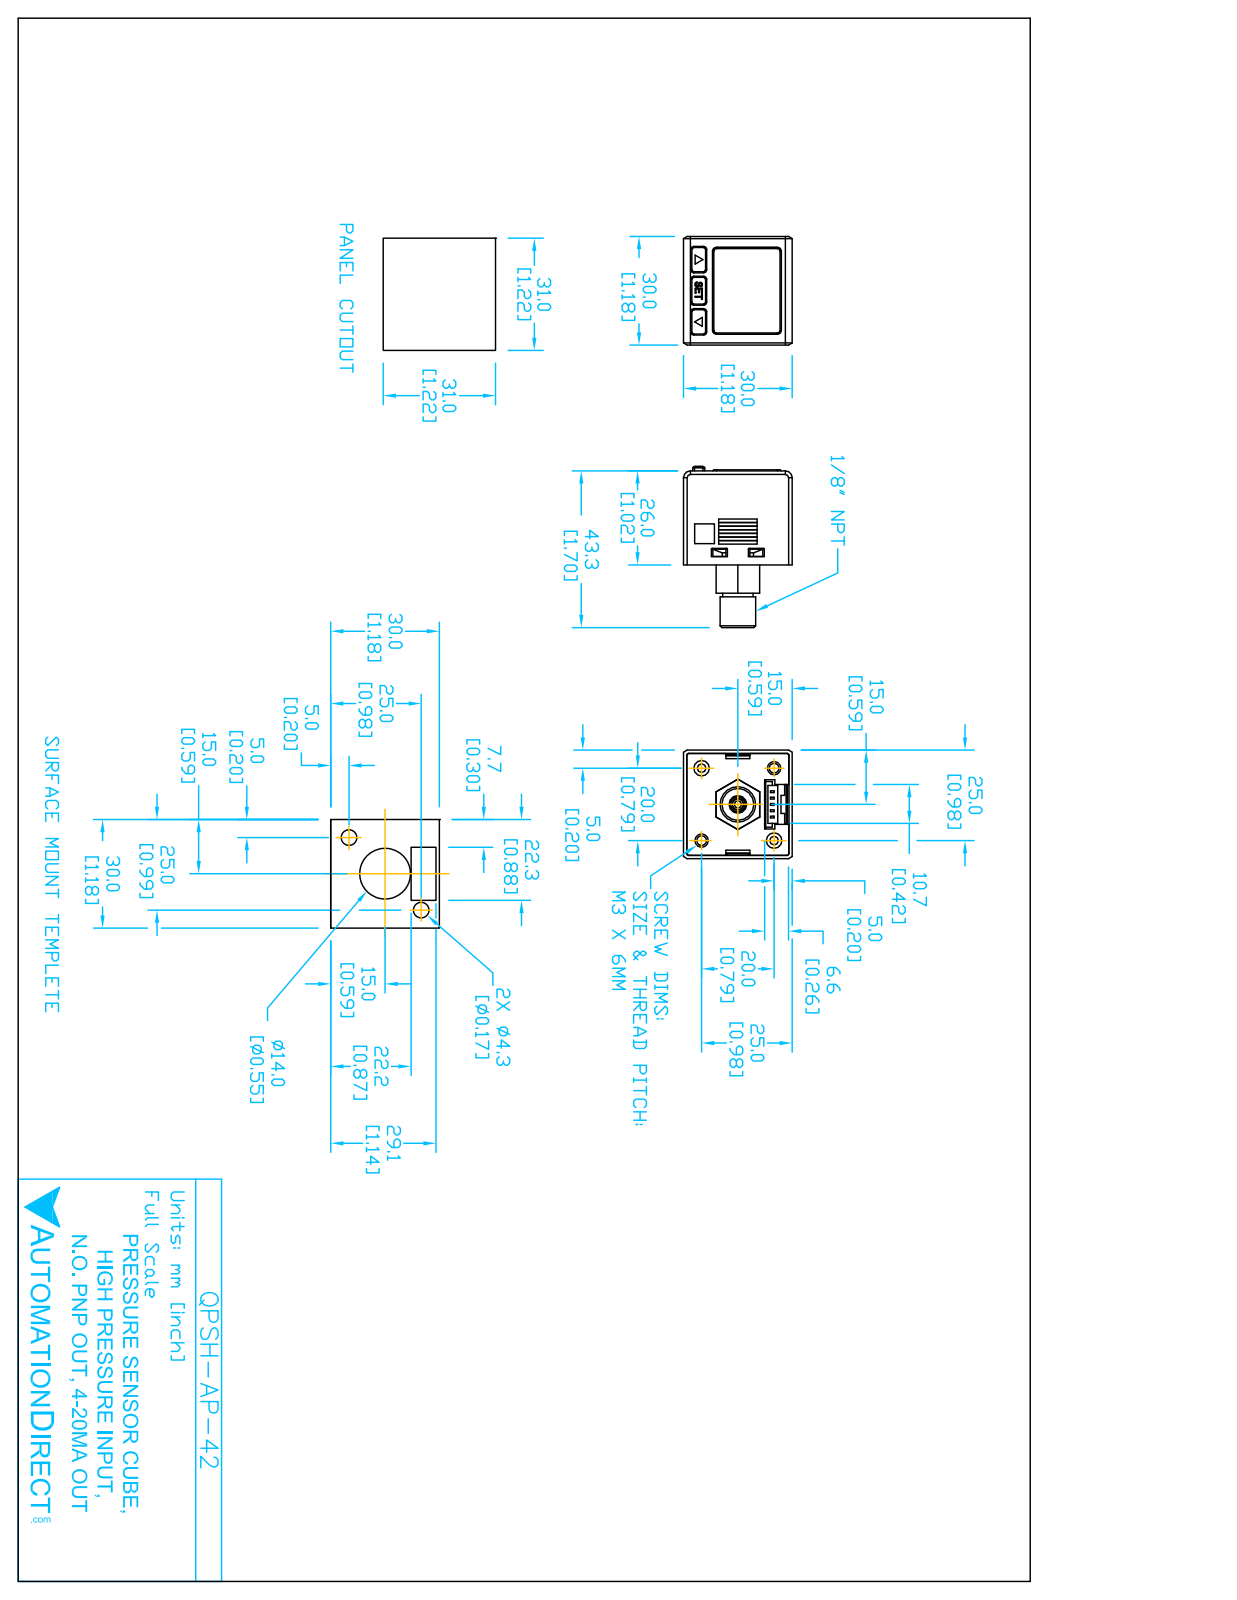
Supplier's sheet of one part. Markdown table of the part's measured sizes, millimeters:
| quantity | value |
| --- | --- |
| part name | QPSH-AP-42 |
| STEP written by | SolidWorks 2014 (AUTOMOTIVE_DESIGN) |
| units | millimeters |
| bodies | 1 solid, 386 faces (296 planar, 62 cylindrical, 28 other) |
| overall size | 45.9 × 30 × 30 |
| volume | 24 520 mm³ |
| surface area | 6 716 mm² |
| round holes (diameter × count) | 2.7 × 2, 3 × 2, 4.8 × 2, 4.2 × 1 |
| round bosses / shafts (diameter × count) | 9.5 × 1, 8.1 × 1 |
| partial cylindrical surfaces (radius × count) | 0.5 × 16, 0.4 × 8, 1.5 × 2 |
| main face-to-face distances | 30, 26.4, 26.4, 0.8, 1, 12.1, 1.3, 14.3, 1.5, 8.9 |
| hole center spacings | 14, 19.8, 28 |
